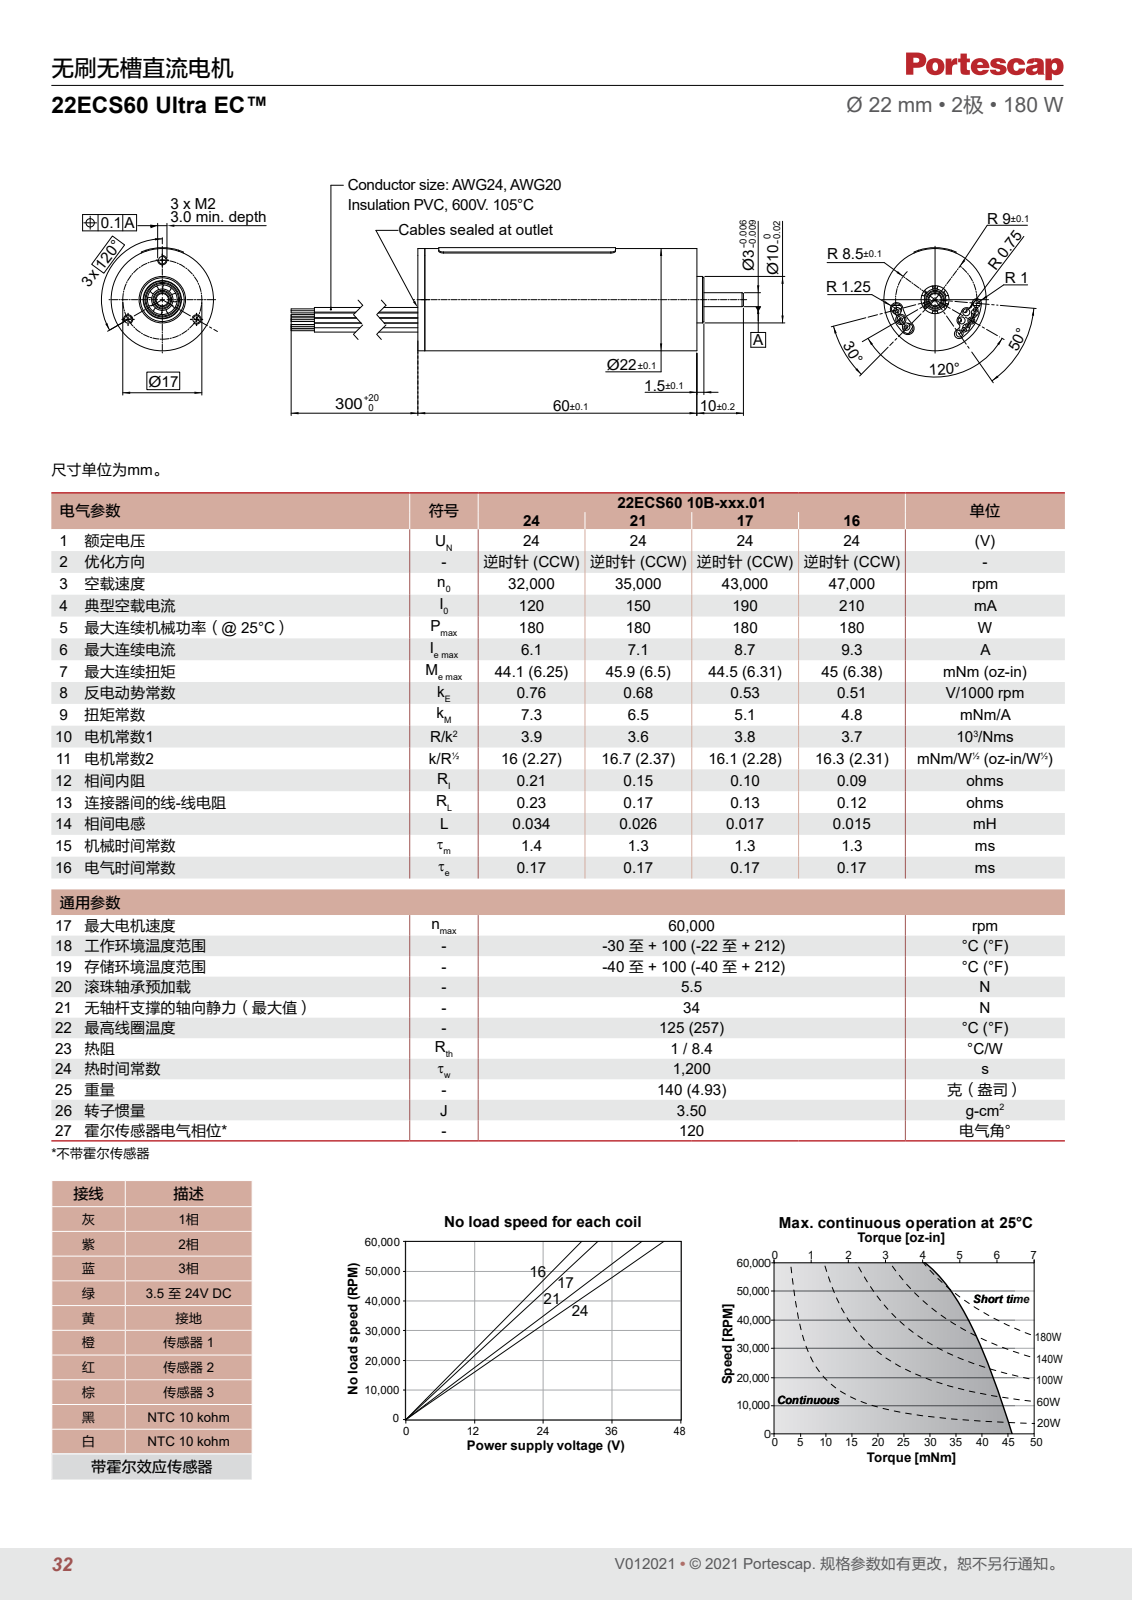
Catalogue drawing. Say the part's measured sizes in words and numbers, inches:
The part is named "22ECS60". Its 3-D file was written by "PRO/ENGINEER BY PARAMETRIC TECHNOLOGY CORPORATION, 2014310 (CONFIG_CONTROL_DESIGN)". It is 17 solids with 374 faces: 86 planar, 170 cylindrical and 118 other. Overall it measures 16.748 by 0.872 by 0.866 inches. Its volume is 1.594 cubic inches and its surface area 26.91 square inches. Round holes: 5 of diameter 0.067, 2 of diameter 0.063, 1 of diameter 0.087, 1 of diameter 0.118, 1 of diameter 0.236, 1 of diameter 0.252, 1 of diameter 0.319, 1 of diameter 0.378, 1 of diameter 0.827. Round bosses or shafts: 7 of diameter 0.039, 7 of diameter 0.016, 3 of diameter 0.063, 3 of diameter 0.028, 1 of diameter 0.866, 1 of diameter 0.394, 1 of diameter 0.315, 1 of diameter 0.181. Partial cylindrical surfaces (rounded edges, fillets, slot ends): 8 of radius 0.039, 2 of radius 0.02, 2 of radius 0.033, 2 of radius 0.043, 2 of radius 0.053, 1 of radius 0.246, 1 of radius 0.281, 1 of radius 0.315. The main face-to-face distances are 2.362, 0.02, 0.059, 0.039, 2.402, 2.343, 2.382, 0.159, 2.203, 2.303. The hole center spacings are 0.335, 0.354, 0.58, 0.065, 0.082, 0.112, 0.144, 0.147.
